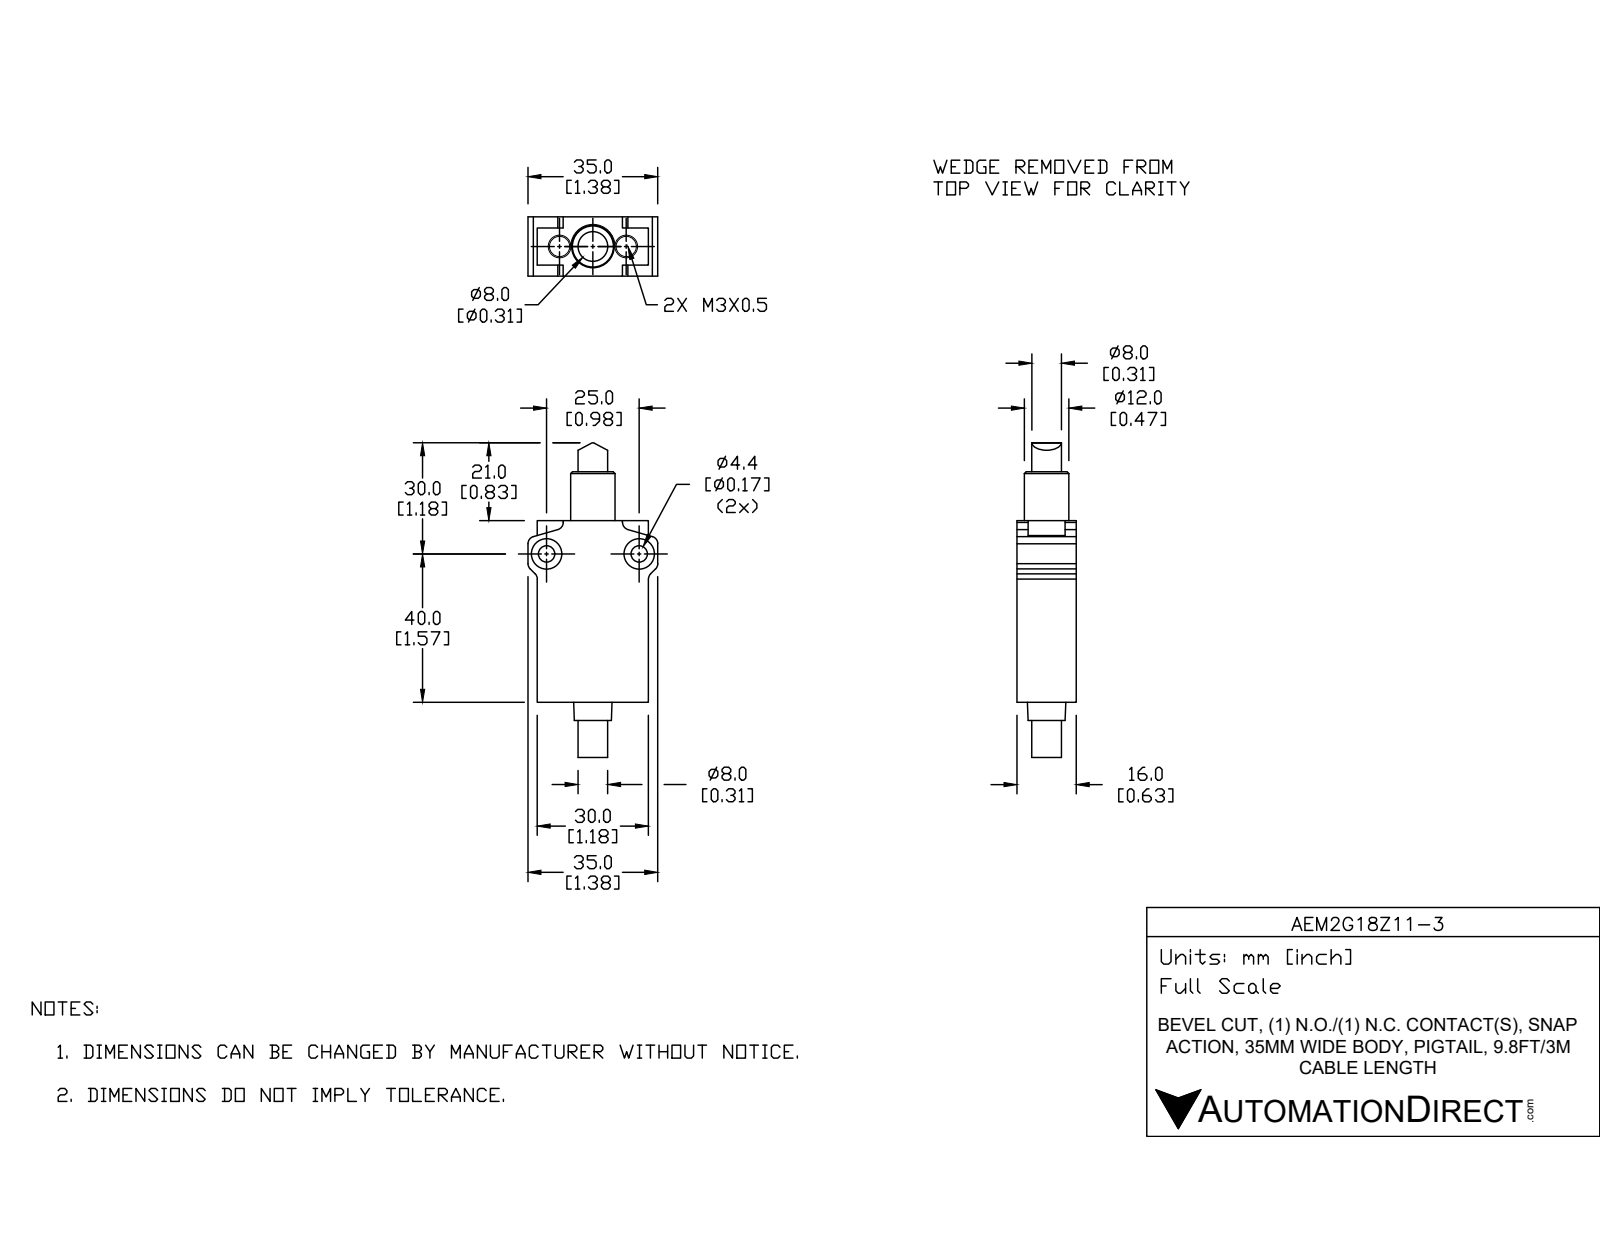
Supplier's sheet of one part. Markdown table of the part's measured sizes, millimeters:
| quantity | value |
| --- | --- |
| part name | AEM2G18Z11-3_Default |
| STEP written by | SolidWorks 2021 (CONFIG_CONTROL_DESIGN) |
| units | millimeters |
| bodies | 3 solids, 103 faces (49 planar, 45 cylindrical, 9 other) |
| overall size | 85.9 × 35 × 16 |
| volume | 25 330 mm³ |
| surface area | 8 781 mm² |
| round holes (diameter × count) | 3 × 2, 4.4 × 2, 8.2 × 2, 8.1 × 1 |
| round bosses / shafts (diameter × count) | 12 × 1, 8 × 1 |
| partial cylindrical surfaces (radius × count) | 2 × 8, 0.8 × 1, 6.5 × 1 |
| main face-to-face distances | 16, 30, 12, 1, 49, 2.5, 32.5, 4, 4.8, 3.8 |
| hole center spacings | 9.5, 19, 25 |
